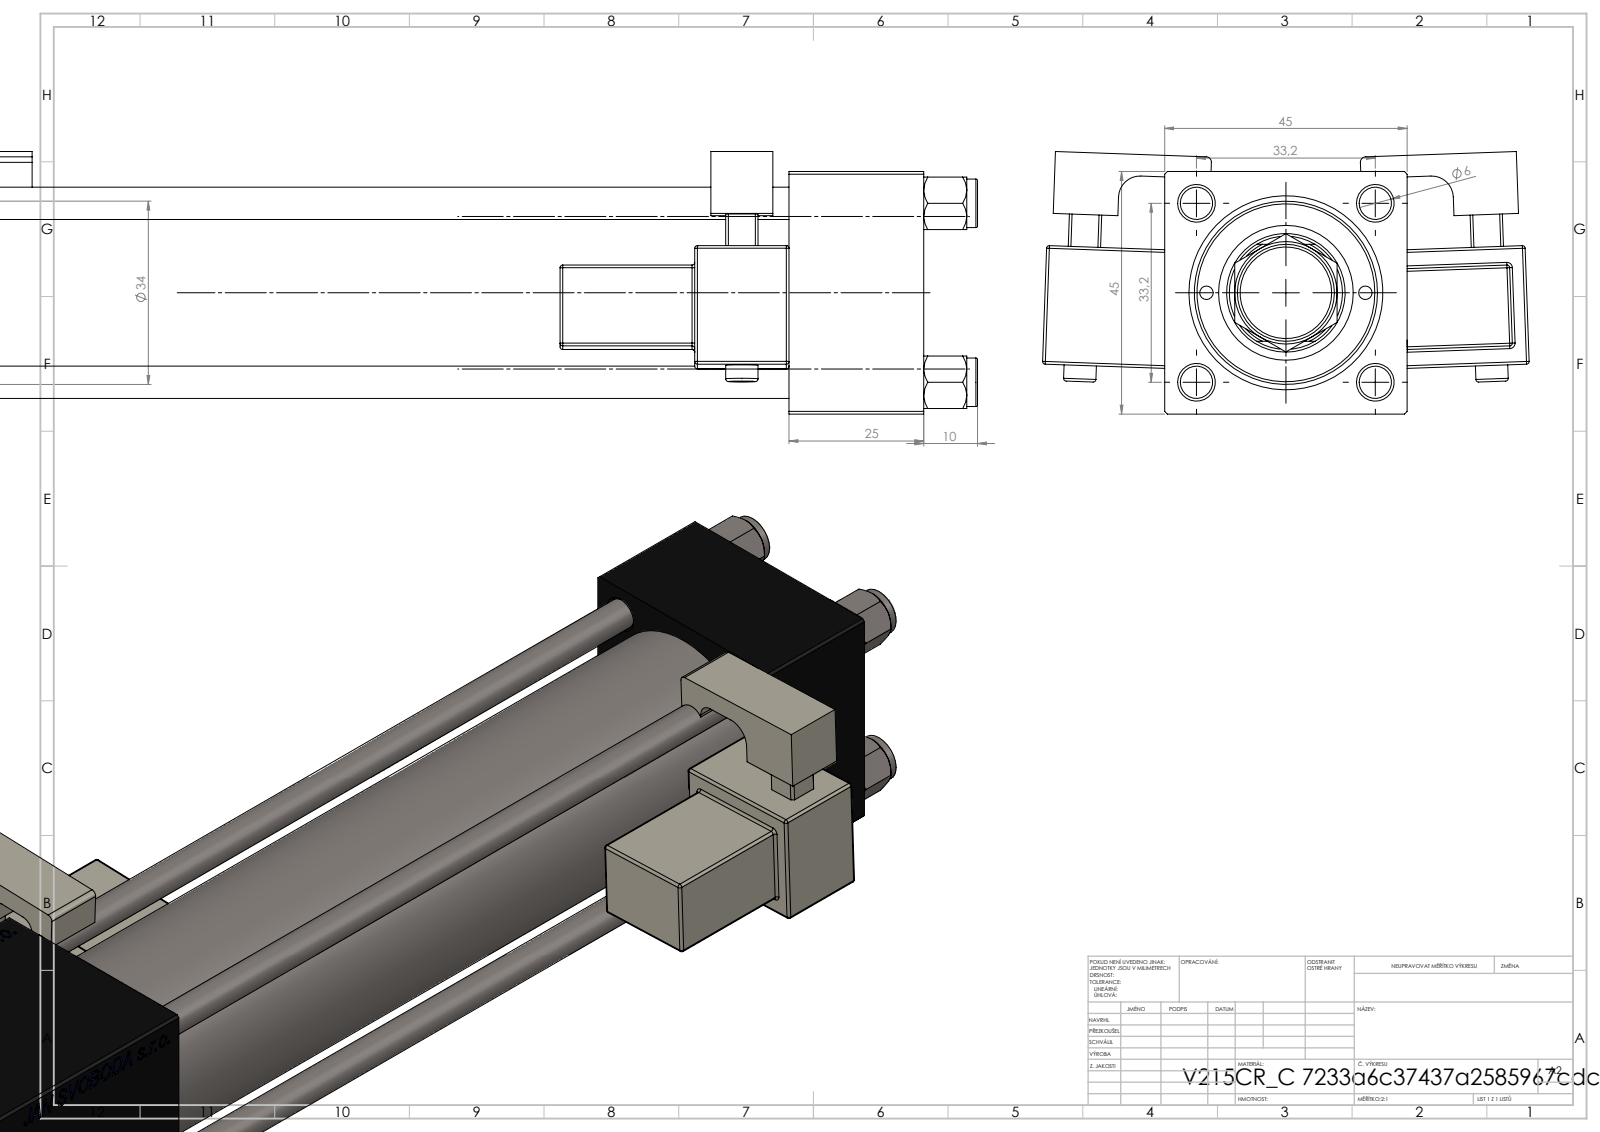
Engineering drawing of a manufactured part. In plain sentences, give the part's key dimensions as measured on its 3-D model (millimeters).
The part is named "V215CR_VCP_C; V215_VC_A; MFA; V215CR_C_Body (+3 more)". Its 3-D file was written by "SolidWorks 2019 (CONFIG_CONTROL_DESIGN)". It is 14 solids with 1363 faces: 605 planar, 154 cylindrical and 604 other. Overall it measures 296 by 90.31 by 48.72 millimeters. Its volume is 344 843 cubic millimeters and its surface area 124 532 square millimeters. Round holes: 4 of diameter 6, 2 of diameter 2.5, 2 of diameter 7, 2 of diameter 13.16, 2 of diameter 20, 1 of diameter 10.5, 1 of diameter 22, 1 of diameter 24, 1 of diameter 25, 1 of diameter 32, 1 of diameter 33. Round bosses or shafts: 4 of diameter 9, 2 of diameter 6, 1 of diameter 38, 1 of diameter 34, 1 of diameter 18, 1 of diameter 11. Partial cylindrical surfaces (rounded edges, fillets, slot ends): 48 of radius 0.5, 2 of radius 1, 2 of radius 2.5, 2 of radius 4, 1 of radius 10.5. The main face-to-face distances are 45, 25, 3, 180, 155, 228, 22.99, 137.5, 203, 13. The hole center spacings are 16.7, 23.48, 33.2, 35.47, 14.75, 46.95, 29.5, 180.5.
